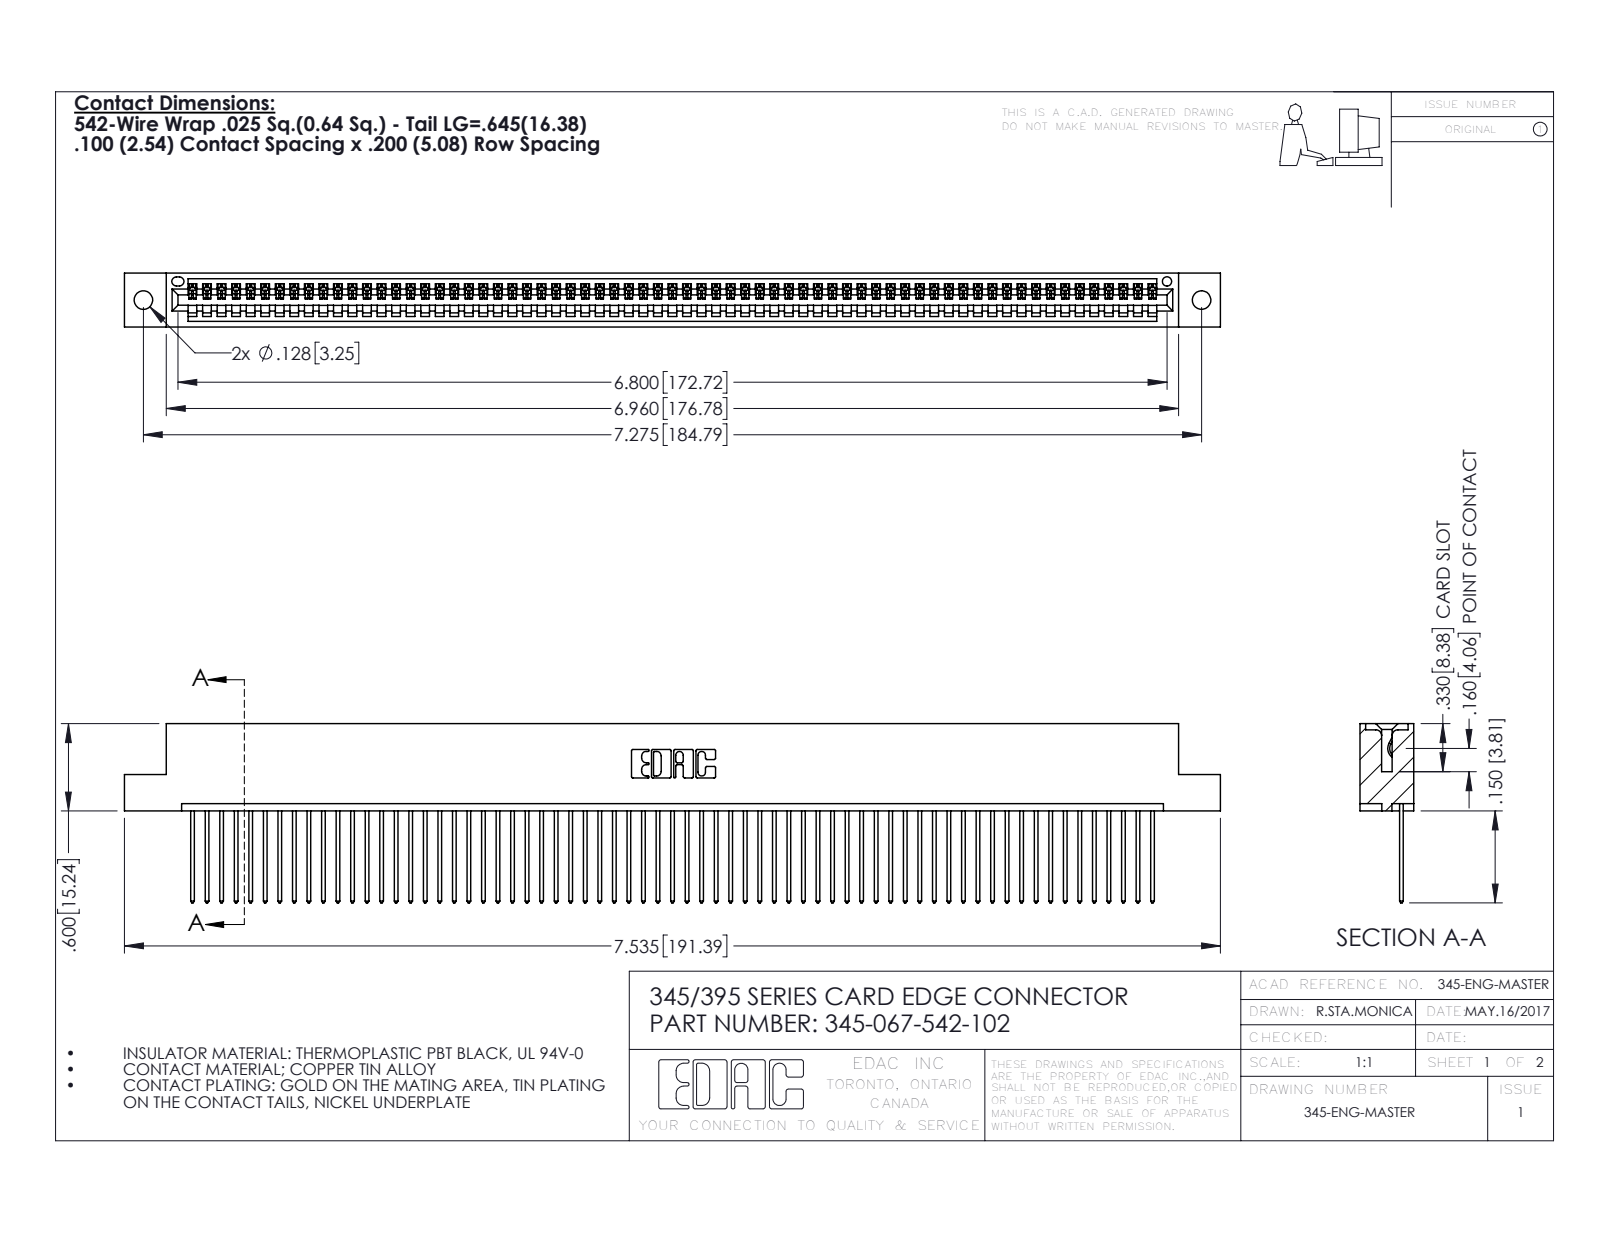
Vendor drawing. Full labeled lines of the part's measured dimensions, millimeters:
Part name (STEP PRODUCT): 345-067-542-102; 345-292-001_345-293-142; 345 Part_Flush Mounting Lugs - 0.128 Dia
STEP written by: SolidWorks 2016 (CONFIG_CONTROL_DESIGN)
Units: millimetres
Bodies: 68 solids, 4012 faces (2760 planar, 1252 cylindrical, 0 other)
Overall size (bounding box): 191.4 × 31.3 × 9.4
Volume: 18 500 mm³ · Surface area: 25 590 mm²
Round holes (diameter × count): ⌀3.3 ×2, ⌀1.6 ×1
Partial cylindrical surfaces — rounded edges, fillets, slot ends (radius × count): R0.2 ×134, R0.3 ×134, R0.3 ×22, R0.2 ×6, R0.8 ×6, R0.7 ×3, R0.8 ×2, R1 ×2
Main face-to-face distances: 1.8, 7.6, 2.5, 6.9, 0.6, 9.4, 5.1, 5.7, 3.8, 1.8
Hole centre spacings: 6.9, 178.8, 184.8
